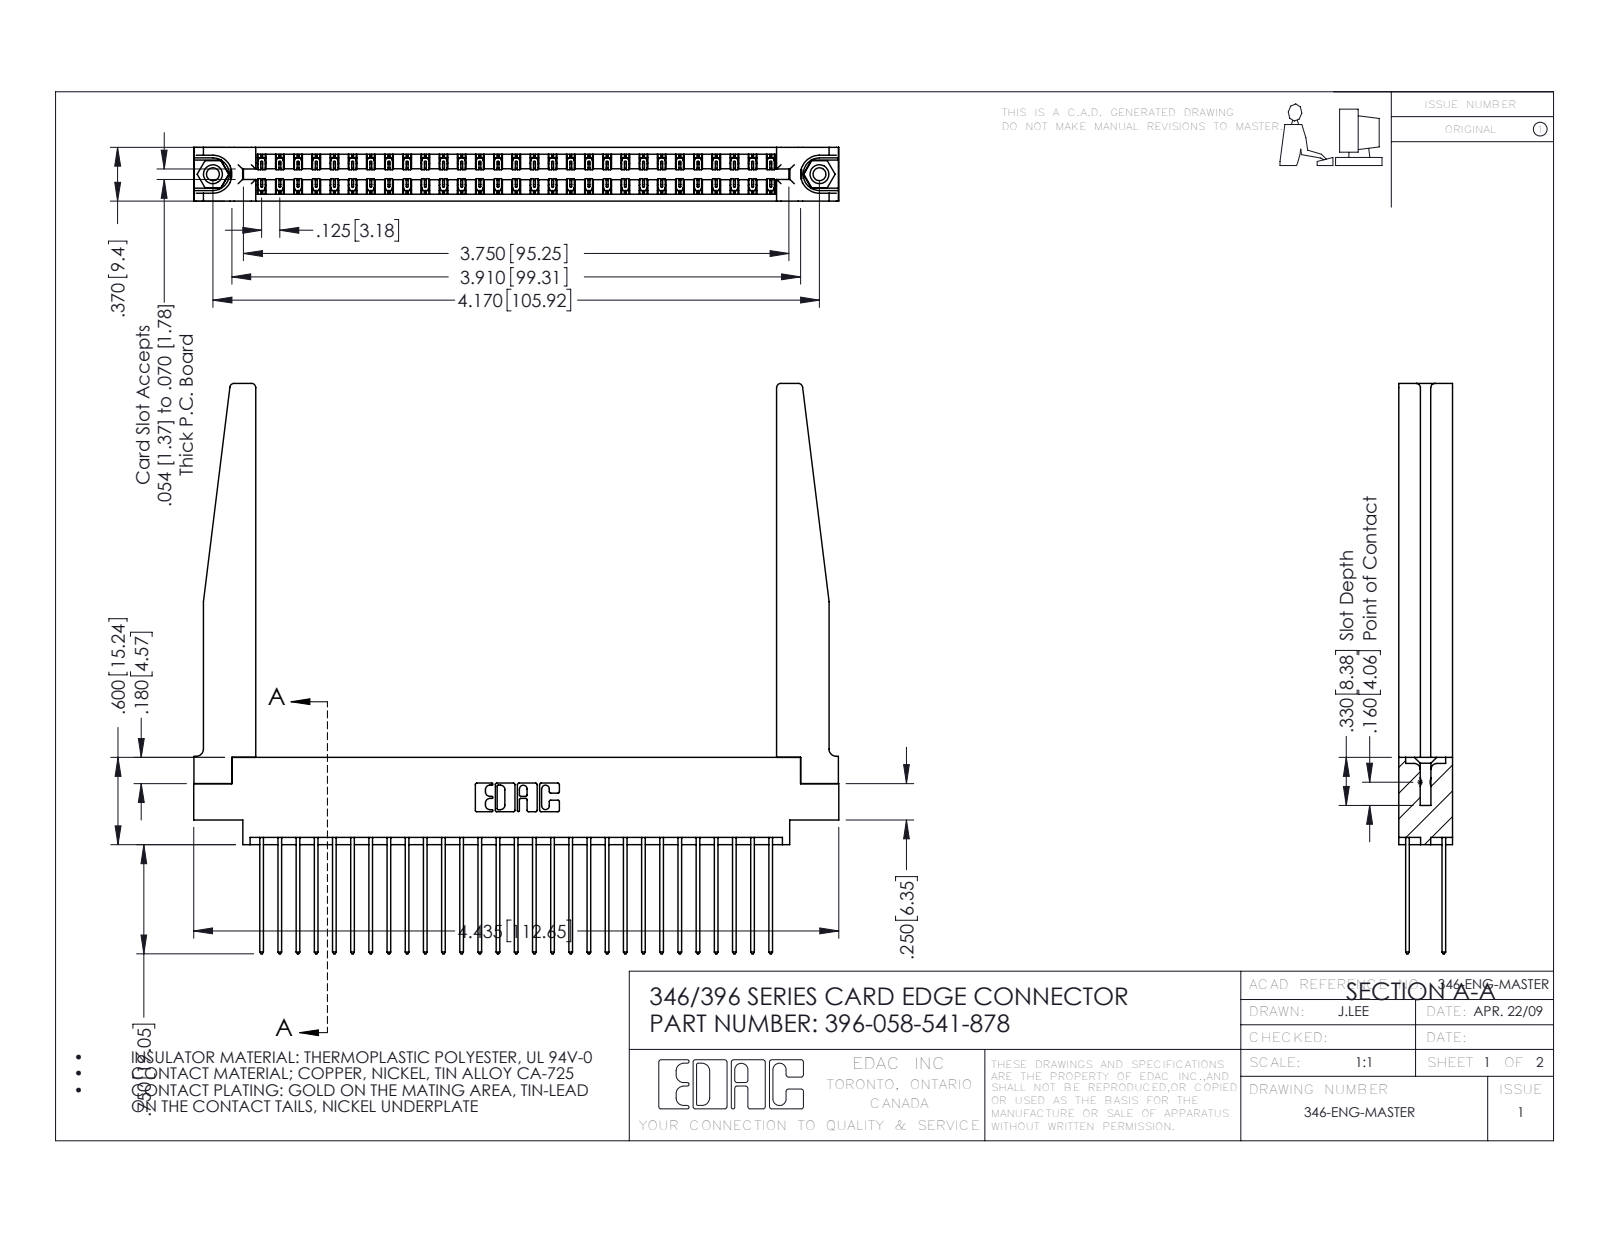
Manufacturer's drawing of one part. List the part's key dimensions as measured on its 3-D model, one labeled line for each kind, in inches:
Part name (STEP PRODUCT): 345-292-001_345-293-141; 345-250-001_345-250-001-102; 396-058-541-878; 346-220-078_345-220-078 (+1 more)
STEP written by: SolidWorks 2016 (CONFIG_CONTROL_DESIGN)
Units: inches
Bodies: 63 solids, 3376 faces (2252 planar, 1072 cylindrical, 52 other)
Overall size (bounding box): 4.435 × 3.92 × 0.37
Volume: 1.097 in³ · Surface area: 36.14 in²
Round holes (diameter × count): ⌀0.089 ×2, ⌀0.125 ×2, ⌀0.156 ×2, ⌀0.064 ×1
Round bosses / shafts (diameter × count): ⌀0.155 ×2
Partial cylindrical surfaces — rounded edges, fillets, slot ends (radius × count): R0.006 ×87, R0.01 ×58, R0.01 ×22, R0.03 ×8, R0.007 ×6, R0.031 ×6, R0.026 ×3, R0.014 ×2
Main face-to-face distances: 0.37, 0.048, 0.322, 0.072, 0.25, 0.298, 0.025, 0.15, 0.148, 0.275
Hole centre spacings: 0.246, 3.962, 4.17
